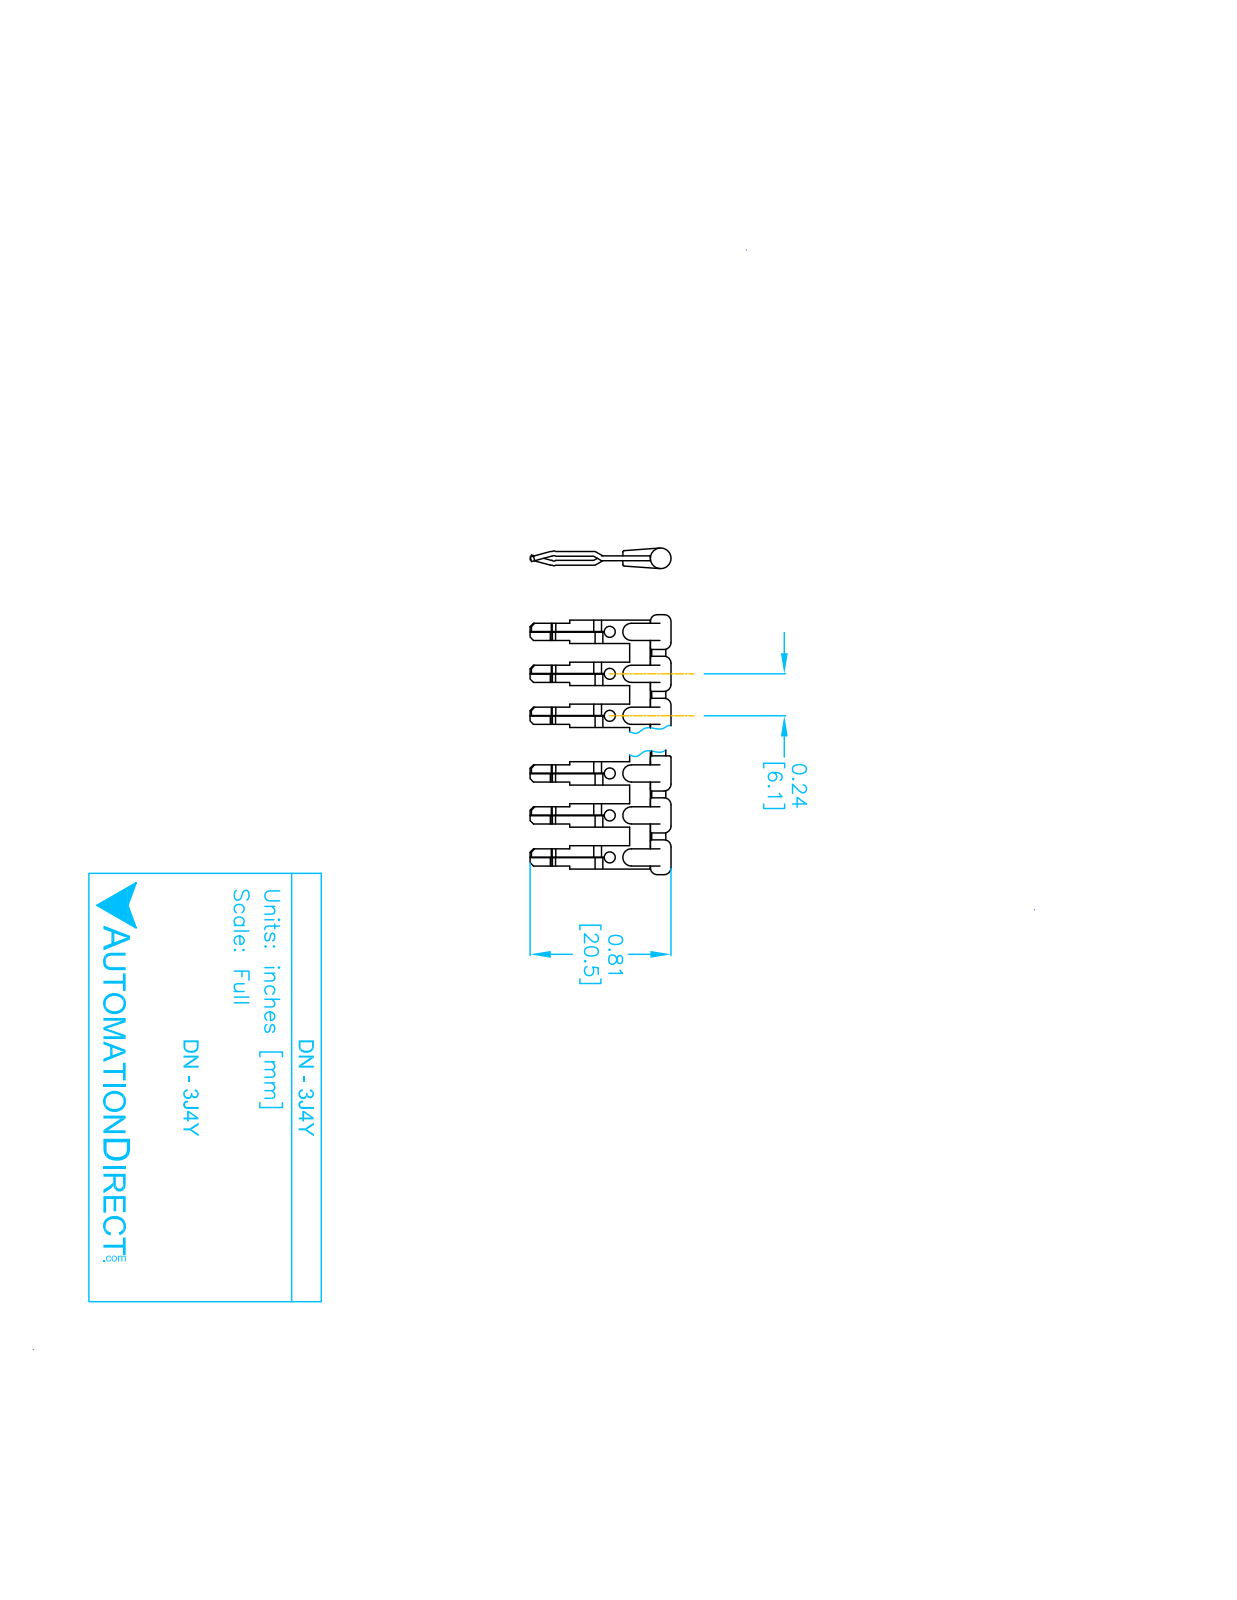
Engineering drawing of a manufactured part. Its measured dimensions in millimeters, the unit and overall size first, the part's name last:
Units: millimetres
Overall size (bounding box): 20.34 × 17.2 × 3
Round holes (diameter × count): ⌀1.3 ×6
Round bosses / shafts (diameter × count): ⌀3 ×1
Partial cylindrical surfaces — rounded edges, fillets, slot ends (radius × count): R0.5 ×12, R0.7 ×4, R1.25 ×3, R0.75 ×1
Main face-to-face distances: 0.7, 0.55, 1.8, 6.1, 3, 1.25, 1.1, 1.3, 4.8, 3.1
Hole centre spacings: 6.1, 7.36, 4.12, 12.2, 12.88
Volume: 300 mm³ · Surface area: 795 mm²
Bodies: 6 solids, 211 faces (123 planar, 61 cylindrical, 27 other)
Part name (STEP PRODUCT): 43520_3_DN-3J4Y; J4_M; J4_N; J4PM_J4 INTERMEDIO (+1 more)
STEP written by: SolidWorks 2013 (AUTOMOTIVE_DESIGN)
